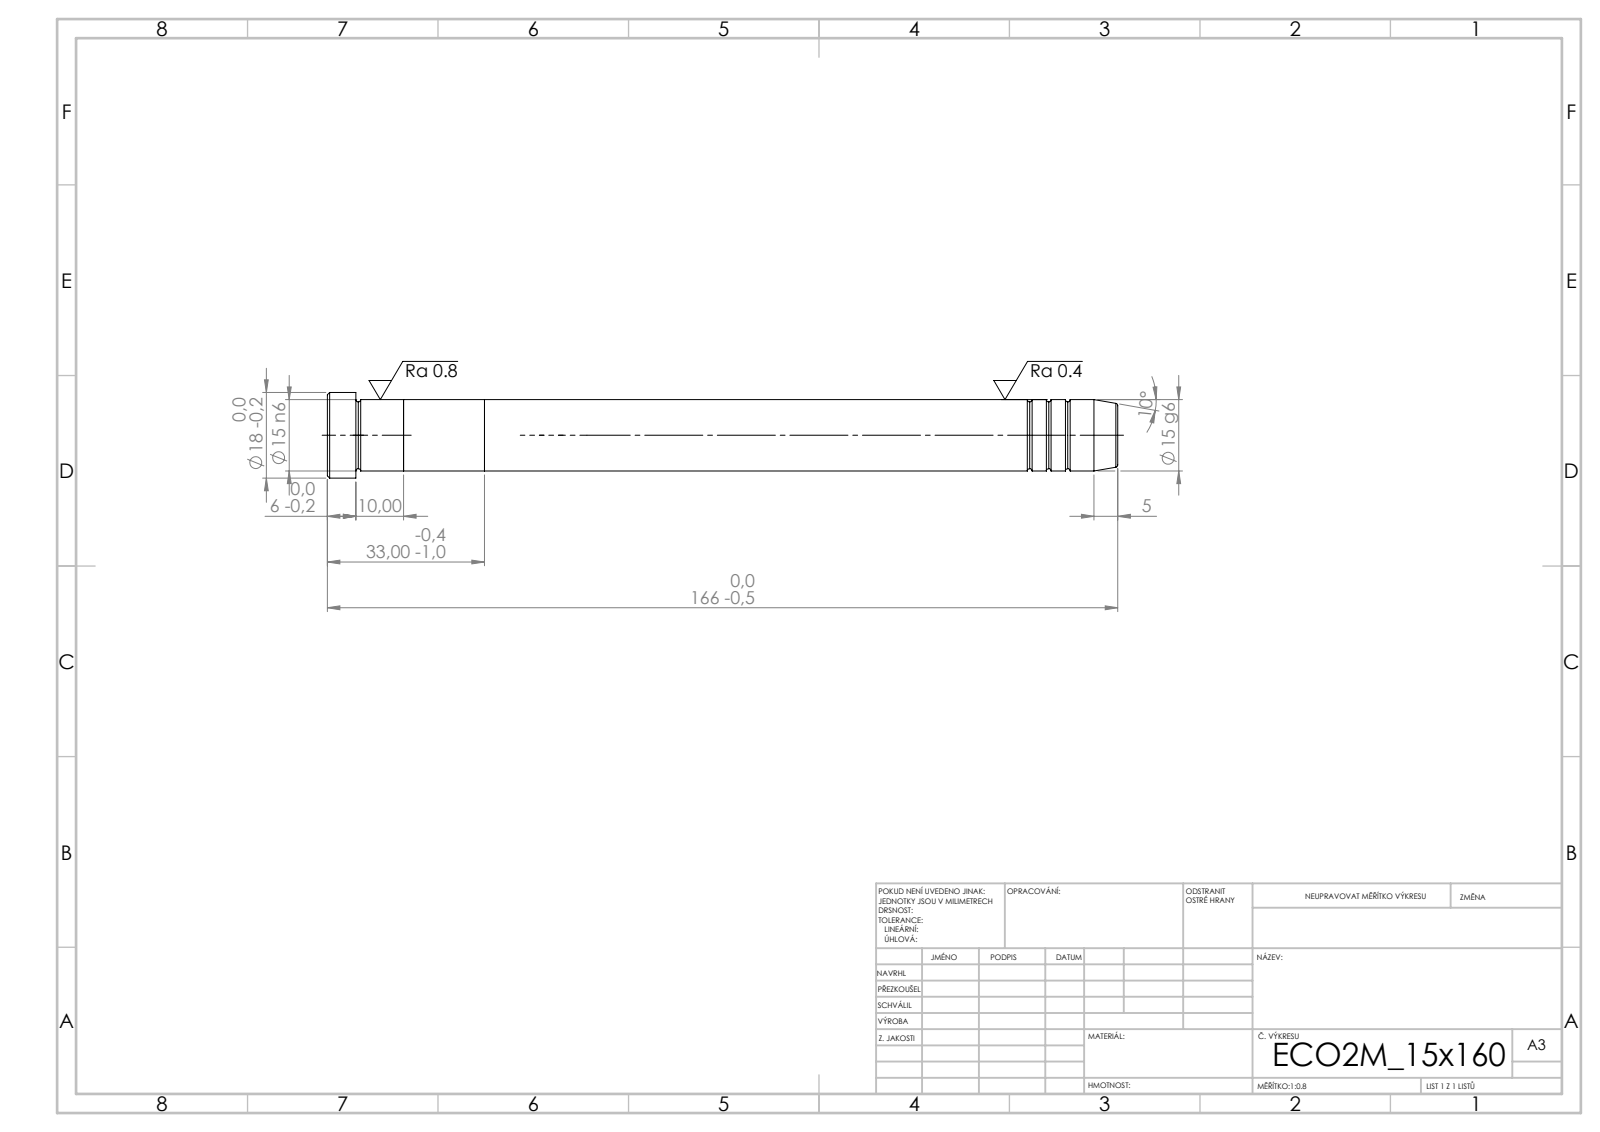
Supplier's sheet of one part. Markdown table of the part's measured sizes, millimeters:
| quantity | value |
| --- | --- |
| STEP written by | SolidWorks 2019 (CONFIG_CONTROL_DESIGN) |
| units | millimeters |
| bodies | 3 solids, 43 faces (7 planar, 14 cylindrical, 22 other) |
| overall size | 166 × 18 × 18 |
| volume | 29 621 mm³ |
| surface area | 9 118 mm² |
| round bosses / shafts (diameter × count) | 18 × 1, 15 × 1 |
| main face-to-face distances | 17, 33, 16, 133, 150, 166, 160, 27, 10, 6 |
